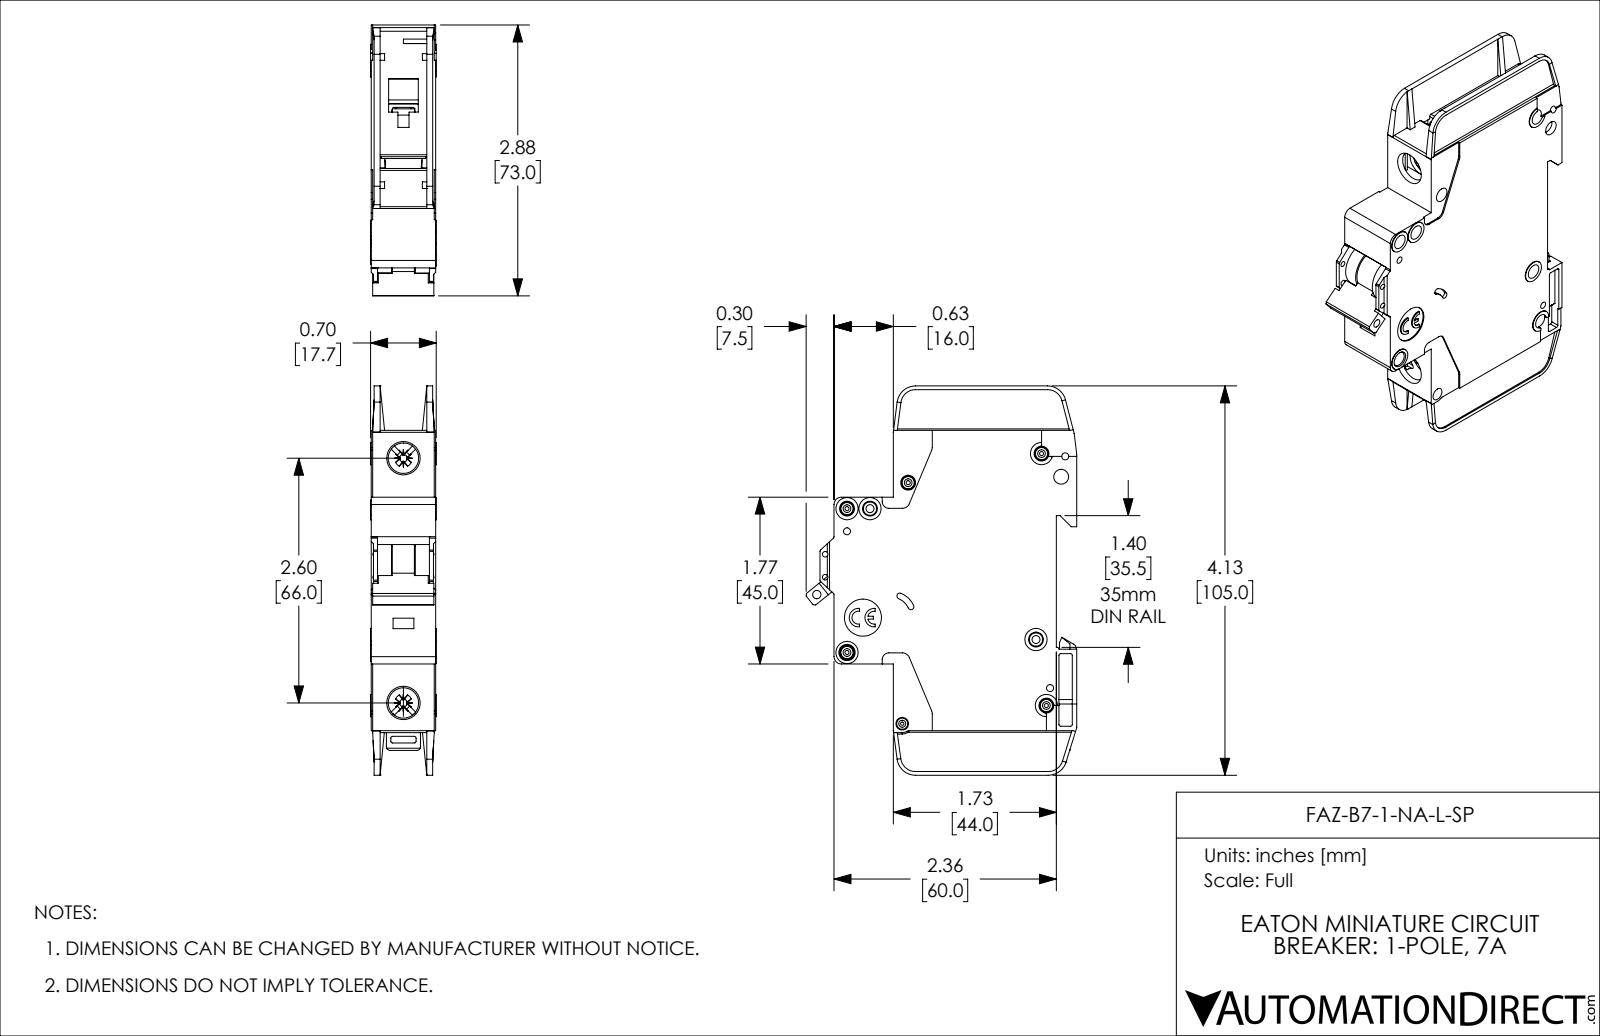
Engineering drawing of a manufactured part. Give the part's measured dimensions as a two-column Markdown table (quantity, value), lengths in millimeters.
| quantity | value |
| --- | --- |
| part name | FAZ-B7-1-NA-L-SP |
| STEP written by | SolidWorks 2019 (AUTOMOTIVE_DESIGN) |
| units | millimeters |
| bodies | 1 solid, 1127 faces (671 planar, 357 cylindrical, 99 other) |
| overall size | 105 × 73.1 × 17.7 |
| volume | 76 720 mm³ |
| surface area | 26 460 mm² |
| round holes (diameter × count) | 4 × 8, 1.1 × 5, 1.9 × 4, 1.5 × 2, 2.2 × 2, 8.2 × 2, 0.9 × 1, 2.3 × 1, 2.5 × 1, 3.4 × 1, 10 × 1 |
| round bosses / shafts (diameter × count) | 3.3 × 5, 6 × 4, 3 × 2, 2.5 × 1 |
| partial cylindrical surfaces (radius × count) | 0.5 × 42, 0.4 × 10, 1 × 10, 2 × 8, 5 × 5, 0.2 × 4, 0.7 × 4, 1.1 × 4 |
| main face-to-face distances | 1.2, 17.4, 15, 16.2, 2.4, 13.8, 0.4, 0.8, 12.6, 14.6 |
| hole center spacings | 6.2, 13.6, 22.1, 4.8, 5.1, 5.2, 5.6, 6.1 |
